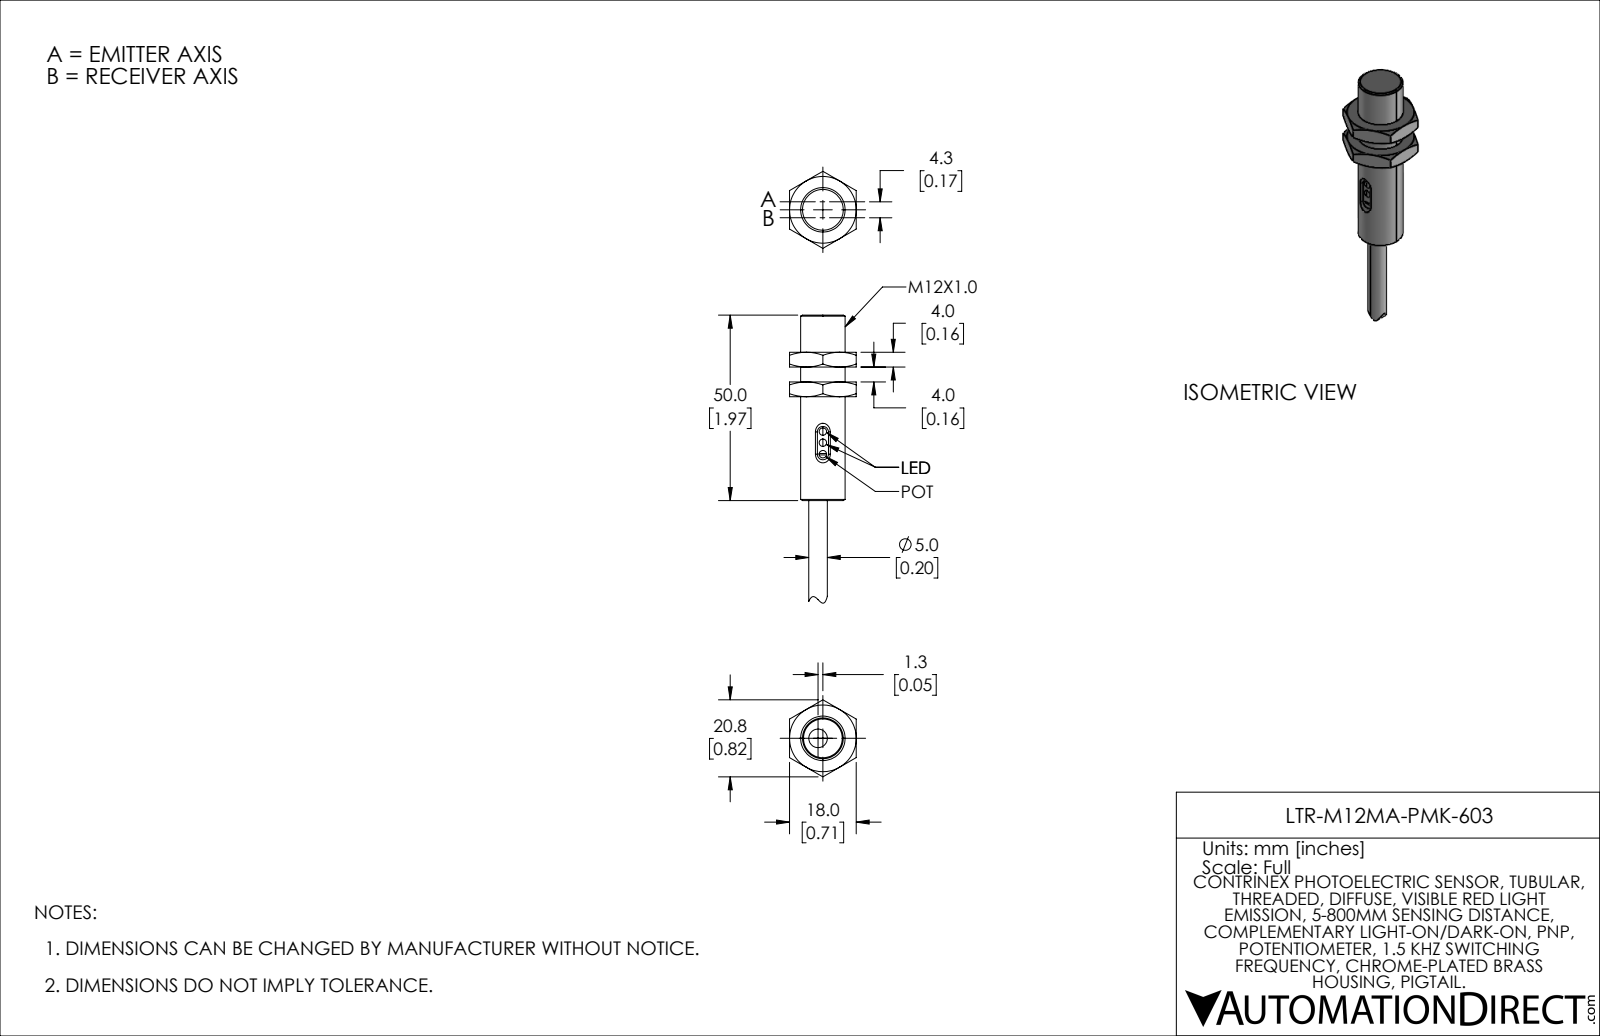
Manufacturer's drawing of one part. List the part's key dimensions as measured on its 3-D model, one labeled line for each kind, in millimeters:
Part name (STEP PRODUCT): LTR-M12MA-PMK-603
STEP written by: SolidWorks 2021 (AUTOMOTIVE_DESIGN)
Units: millimetres
Bodies: 5 solids, 104 faces (31 planar, 20 cylindrical, 53 other)
Overall size (bounding box): 77.68 × 20.79 × 18
Volume: 8 524 mm³ · Surface area: 4 505 mm²
Round holes (diameter × count): ⌀10.2 ×1, ⌀12 ×1
Round bosses / shafts (diameter × count): ⌀5 ×1
Partial cylindrical surfaces — rounded edges, fillets, slot ends (radius × count): R1.5 ×2, R1 ×1
Main face-to-face distances: 10, 18, 6, 16, 4, 40, 34, 30, 24, 20
